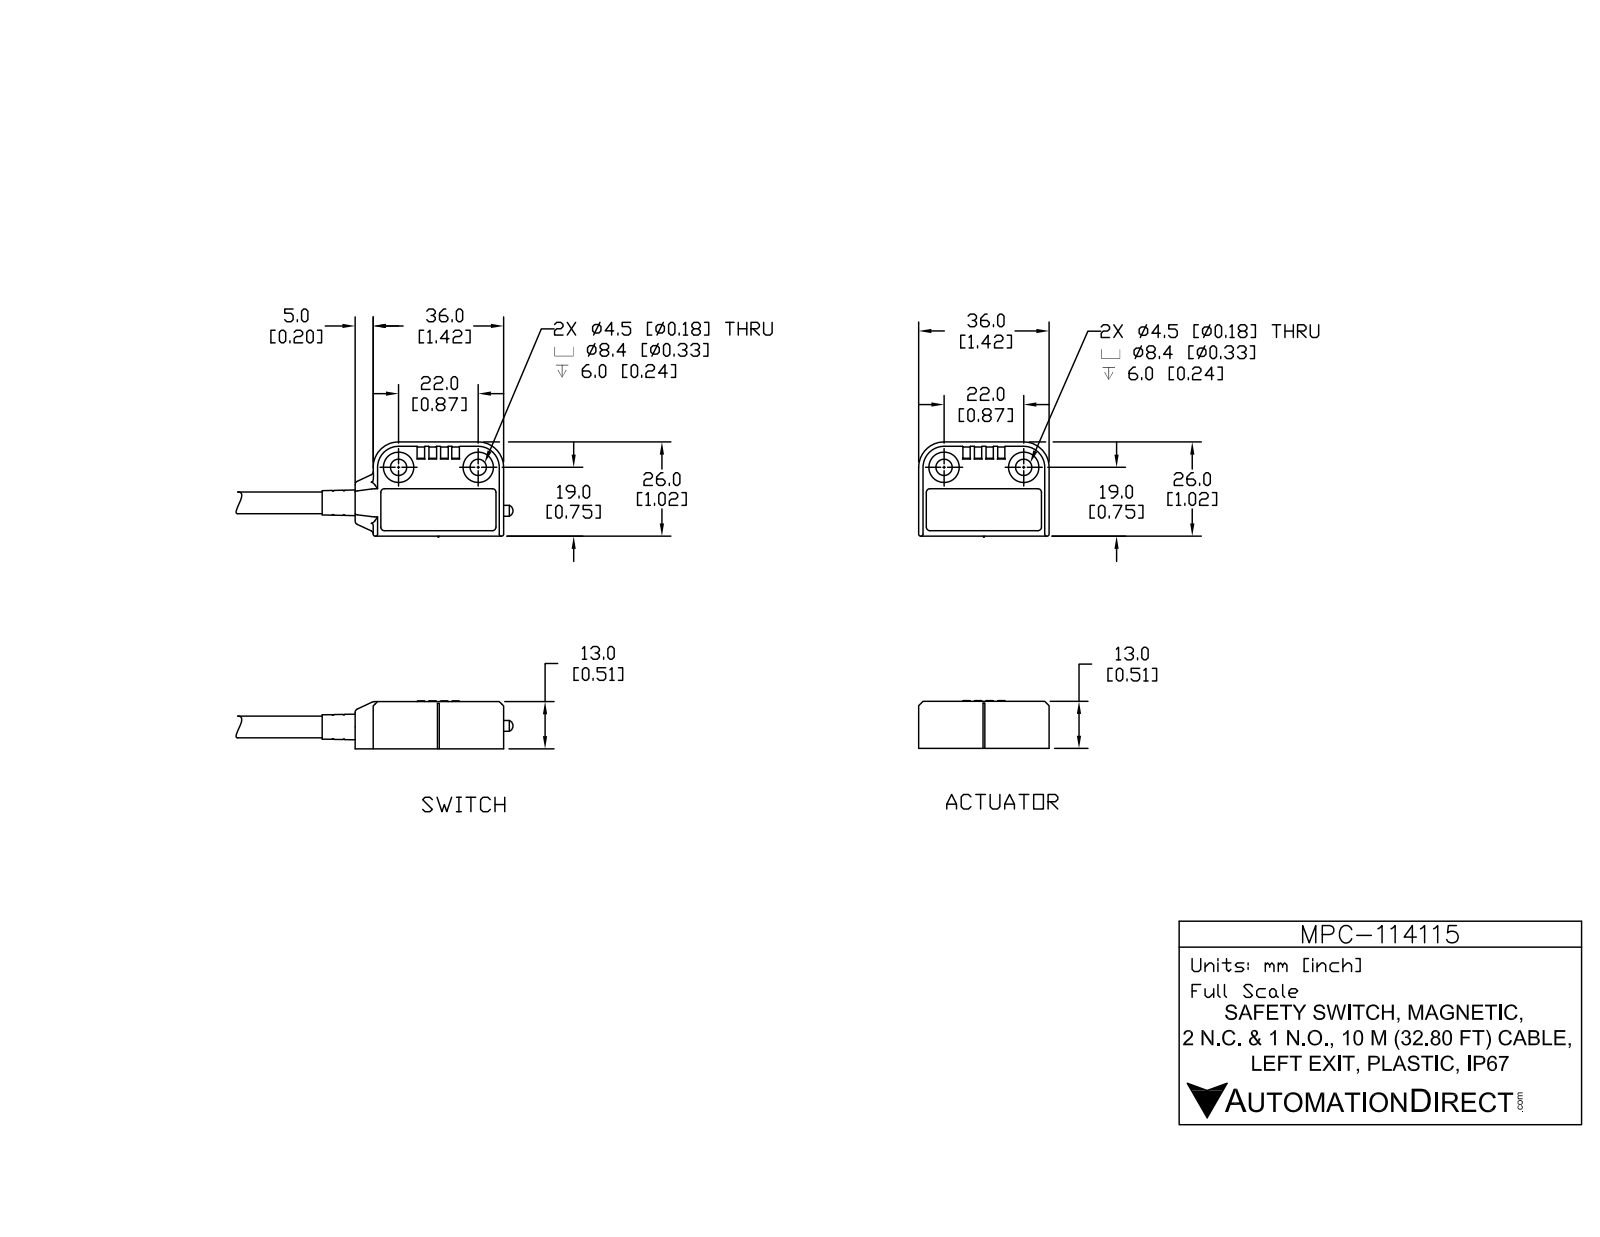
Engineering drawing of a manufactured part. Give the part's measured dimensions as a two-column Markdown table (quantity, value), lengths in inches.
| quantity | value |
| --- | --- |
| part name | MPC-114115_2; MPC-114115_1; MPC-114115 |
| STEP written by | SolidWorks 2017 (AUTOMOTIVE_DESIGN) |
| units | inches |
| bodies | 10 solids, 1067 faces (453 planar, 346 cylindrical, 268 other) |
| overall size | 7.748 × 2.087 × 0.528 |
| volume | 1.065 in³ |
| surface area | 29.75 in² |
| round holes (diameter × count) | 0.177 × 4, 0.331 × 4, 0.195 × 2, 0.098 × 1, 0.118 × 1, 0.197 × 1, 0.232 × 1, 0.244 × 1, 0.291 × 1 |
| round bosses / shafts (diameter × count) | 0.236 × 2, 0.197 × 2, 0.091 × 2, 0.079 × 2, 0.031 × 2, 0.339 × 1, 0.299 × 1, 0.28 × 1 |
| partial cylindrical surfaces (radius × count) | 0.02 × 84, 0.012 × 32, 0.008 × 30, 0.004 × 17, 0.039 × 13, 0.169 × 4, 0.201 × 4, 0.276 × 4 |
| main face-to-face distances | 0.055, 0.508, 0.449, 0.461, 0.059, 0.047, 1.063, 0.496, 0.445, 0.031 |
| hole center spacings | 0.866, 0.434, 0.445, 0.974, 1.091, 1.152, 1.393, 1.535 |
